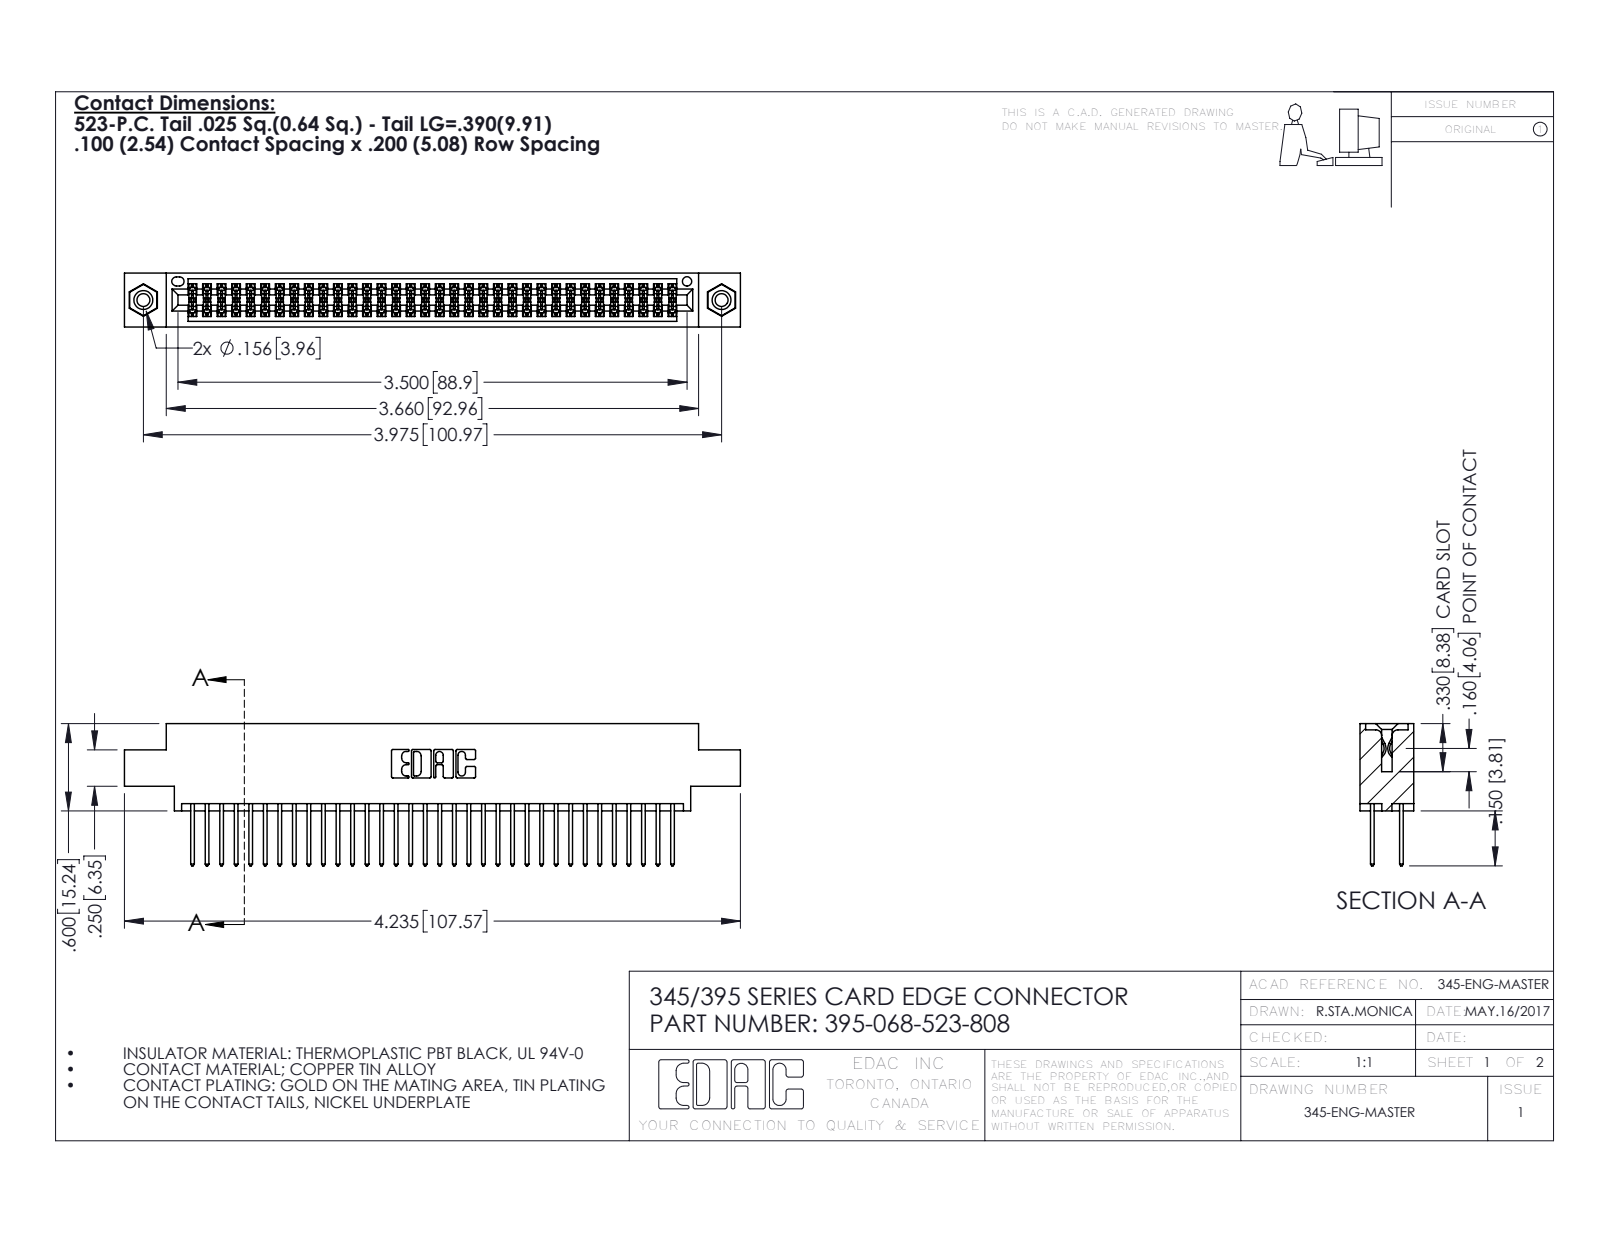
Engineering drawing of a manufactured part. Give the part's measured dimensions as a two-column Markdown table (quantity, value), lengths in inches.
| quantity | value |
| --- | --- |
| part name | 345-250-001_345-250-003-102; 345 Part_0.170 Offset - 0.156 Dia-TI; 345-292-001_345-293-123; 395-068-523-808 |
| STEP written by | SolidWorks 2016 (CONFIG_CONTROL_DESIGN) |
| units | inches |
| bodies | 71 solids, 3590 faces (2360 planar, 1214 cylindrical, 16 other) |
| overall size | 4.235 × 0.977 × 0.37 |
| volume | 0.634 in³ |
| surface area | 24.79 in² |
| round holes (diameter × count) | 0.089 × 2, 0.125 × 2, 0.156 × 2, 0.064 × 1 |
| round bosses / shafts (diameter × count) | 0.155 × 2 |
| partial cylindrical surfaces (radius × count) | 0.006 × 102, 0.01 × 68, 0.01 × 22, 0.007 × 6, 0.031 × 6, 0.026 × 3, 0.014 × 2, 0.019 × 2 |
| main face-to-face distances | 0.072, 0.298, 0.2, 0.098, 0.272, 0.025, 0.37, 0.225, 0.175, 0.149 |
| hole center spacings | 0.27, 3.74, 3.975 |
